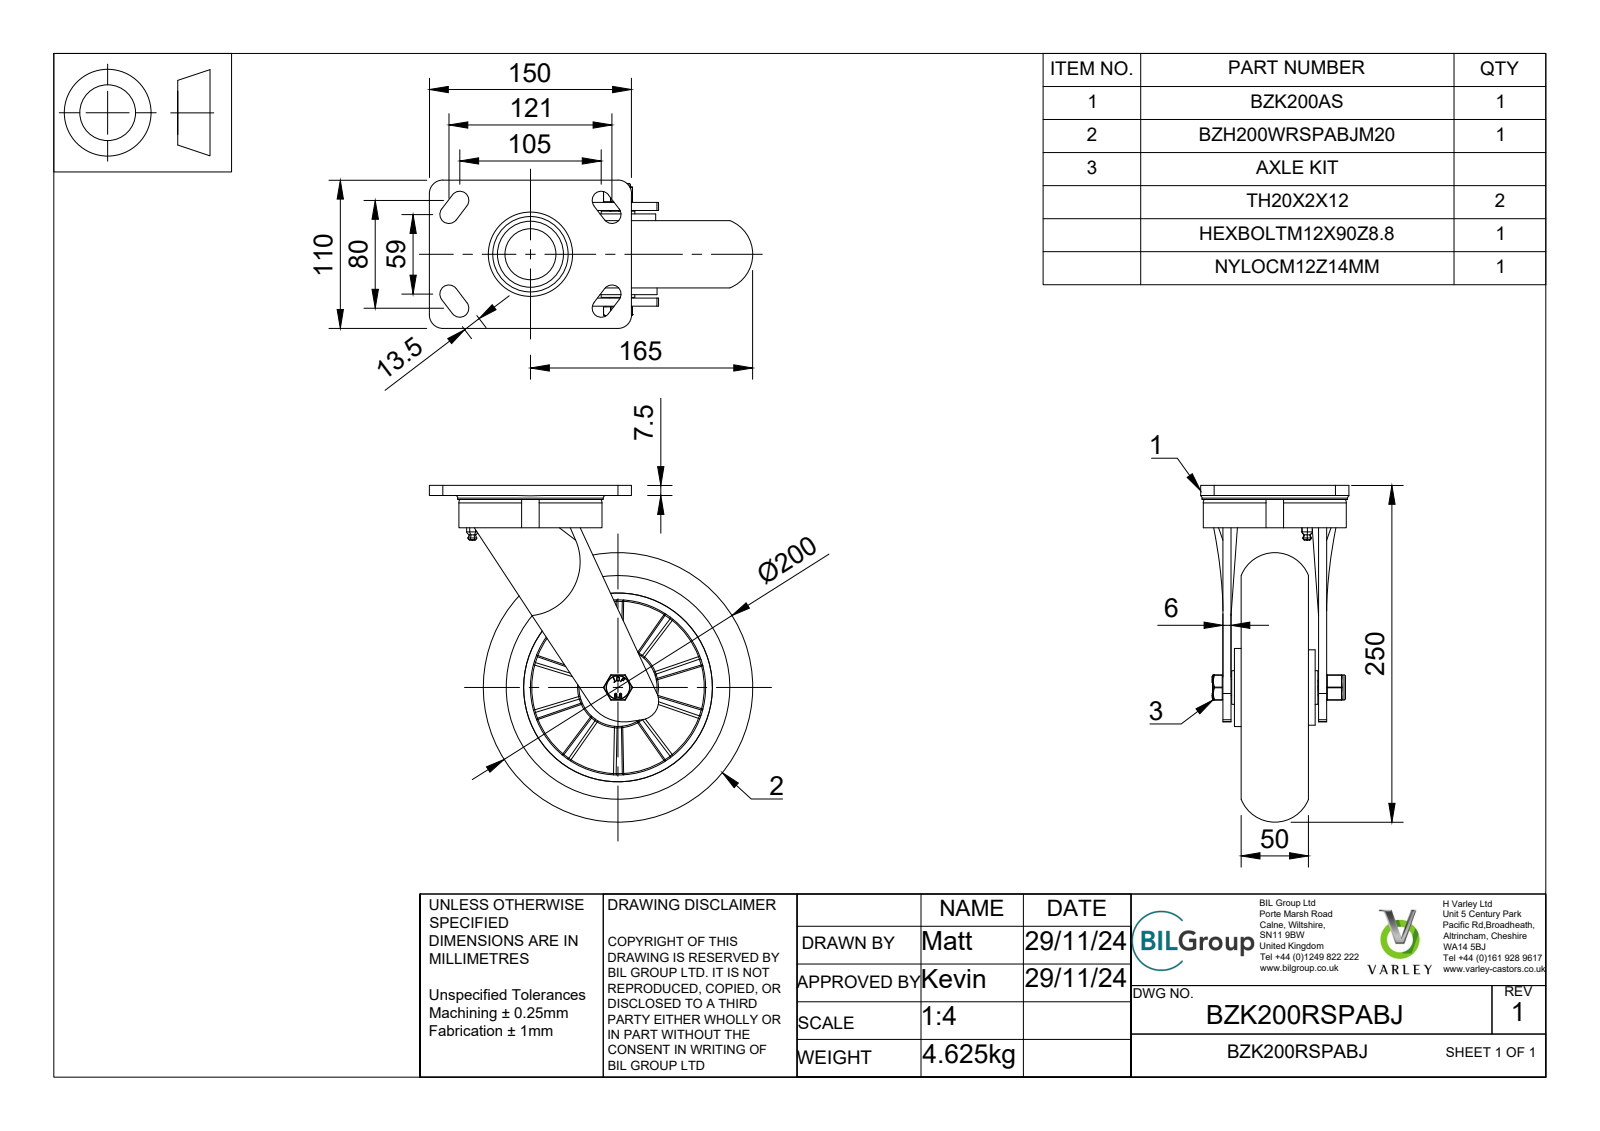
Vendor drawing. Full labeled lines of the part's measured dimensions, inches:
Part name (STEP PRODUCT): BZK200RSPABJ v4; BZK200AS v1; FABRICATED STEEL FORKS; FABRICATED STEEL FORKS Geometry (+8 more)
STEP written by: Autodesk Translation Framework v13.20.0.188 (AP242_MANAGED_MODEL_BASED_3D_ENGINEERING_MIM_LF)
Units: inches
Bodies: 37 solids, 1310 faces (445 planar, 202 cylindrical, 663 other)
Overall size (bounding box): 9.843 × 9.449 × 4.331
Volume: 79.94 in³ · Surface area: 526.6 in²
Round holes (diameter × count): ⌀0.472 ×1, ⌀0.48 ×1, ⌀0.512 ×1, ⌀0.551 ×1, ⌀0.787 ×1, ⌀1.122 ×1, ⌀1.213 ×1, ⌀1.496 ×1, ⌀1.587 ×1, ⌀1.594 ×1, ⌀1.654 ×1, ⌀1.85 ×1
Round bosses / shafts (diameter × count): ⌀4.252 ×1, ⌀4.213 ×1, ⌀2.283 ×1, ⌀2.205 ×1, ⌀1.606 ×1, ⌀1.232 ×1, ⌀1.063 ×1, ⌀0.984 ×1
Partial cylindrical surfaces — rounded edges, fillets, slot ends (radius × count): R0.02 ×18, R0.266 ×8, R0.019 ×4, R0.035 ×4, R0.394 ×4, R0.035 ×2, R0.035 ×2, R0.267 ×2
Main face-to-face distances: 0.295, 0.65, 0.531, 2.795, 0.354, 0.276, 0.886, 2.5, 0.236, 2.264
